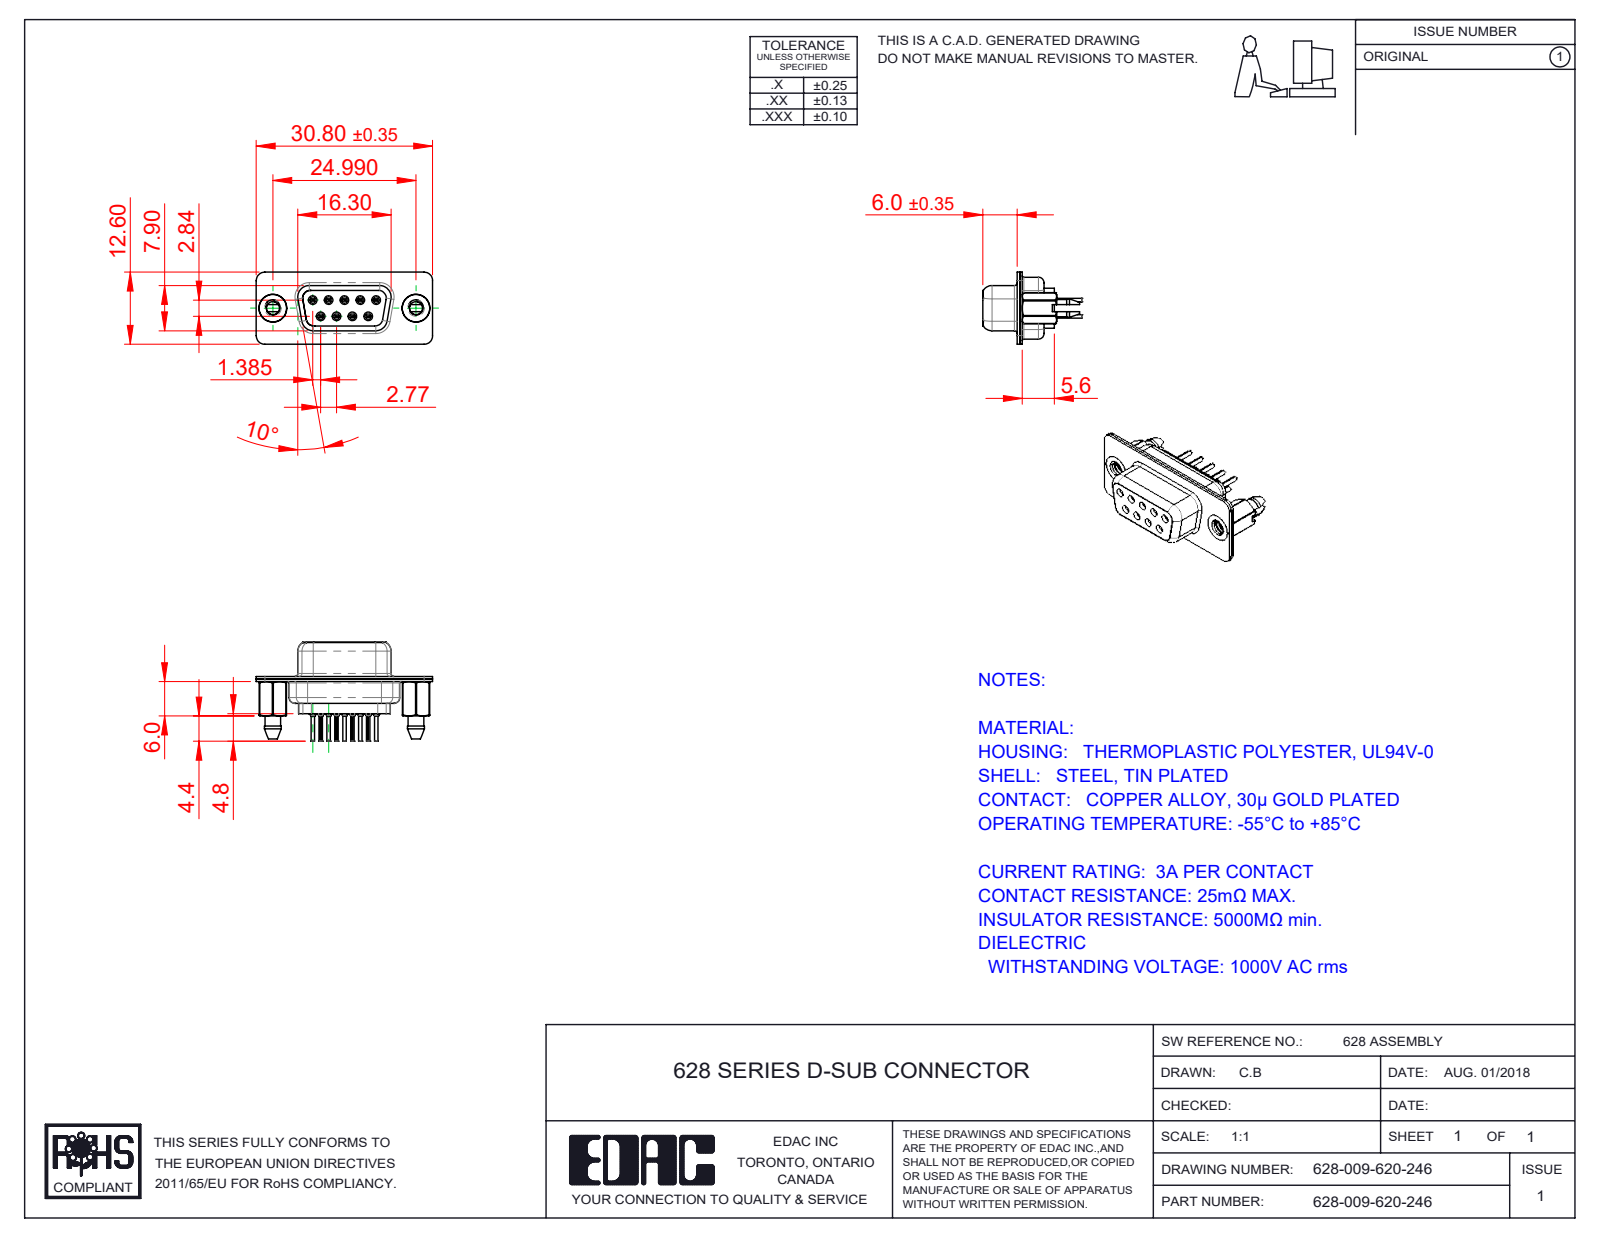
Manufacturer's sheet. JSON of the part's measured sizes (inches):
{"part_name": "628 Contact Row 1_20L; 628 Housing_09 LP; 628 4-40 Threaded Boardlock_LP; 628 Shell Front_09 Contacts (+3 more)", "step_written_by": "SolidWorks 2020 (CONFIG_CONTROL_DESIGN)", "units": "inches", "bodies": {"solids": 14, "faces": 1496, "planar": 378, "cylindrical": 466, "other": 652}, "overall_size": [1.213, 0.681, 0.496], "volume_in3": 0.114, "surface_area_in2": 7.438, "round_holes": [[0.008, 9], [0.031, 9], [0.035, 9], [0.043, 9], [0.063, 9], [0.067, 5], [0.089, 2], [0.157, 2], [0.159, 2], [0.191, 2]], "round_bosses_or_shafts": [[0.079, 9], [0.059, 9], [0.047, 9], [0.024, 9], [0.195, 2], [0.189, 2]], "partial_cylinders_radius": [[0.059, 19], [0.004, 18], [0.079, 12], [0.011, 9], [0.053, 6], [0.063, 6], [0.01, 4], [0.02, 4]], "face_to_face_distances": [0.018, 0.016, 0.035, 0.075, 0.335, 0.26, 0.055, 0.02, 0.256, 0.492], "hole_center_spacings": [0.124, 0.109, 0.218, 0.198, 0.198, 0.327, 0.294, 0.295]}
